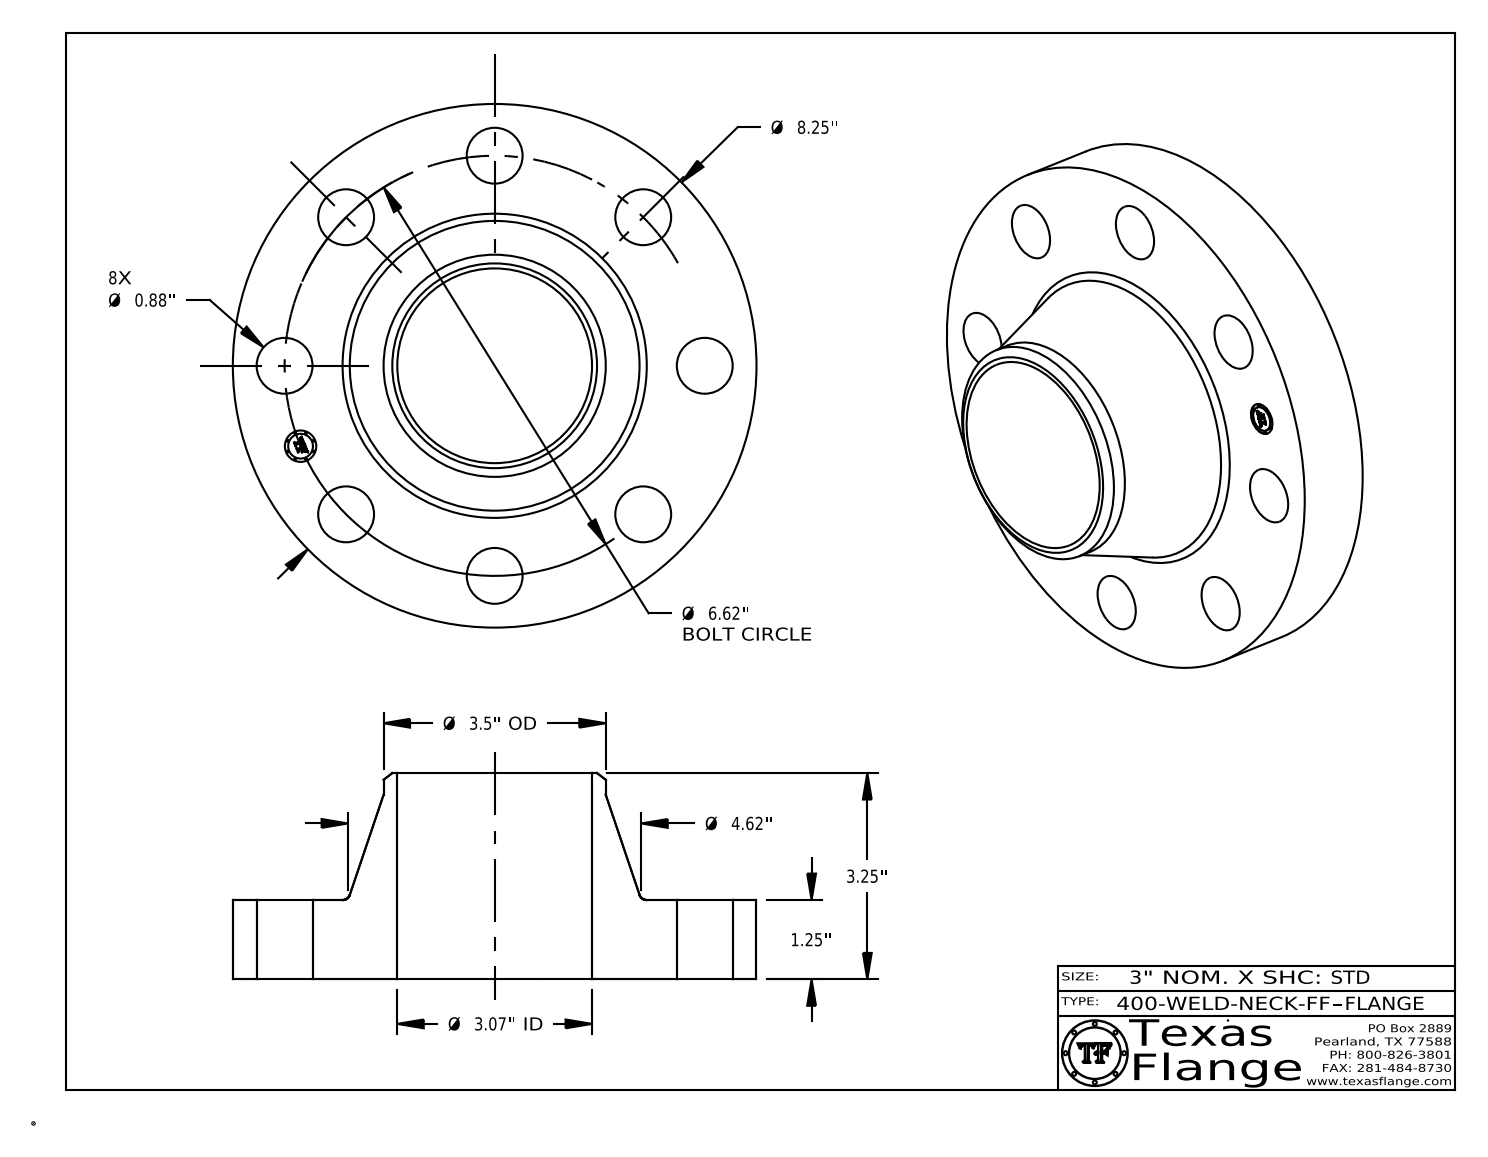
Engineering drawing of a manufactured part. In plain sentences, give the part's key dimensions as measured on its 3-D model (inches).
The part is named "400-WELD-NECK-FF". Its 3-D file was written by "CATIA V5 STEP AP214 (AUTOMOTIVE_DESIGN)". It is 1 solid with 416 faces: 368 planar, 42 cylindrical and 6 other. Overall it measures 8.25 by 8.25 by 3.25 inches. Its volume is 61.55 cubic inches and its surface area 191.7 square inches. Round holes: 8 of diameter 0.88, 1 of diameter 0.495, 1 of diameter 3.068. Round bosses or shafts: 8 of diameter 0.03, 1 of diameter 8.25, 1 of diameter 3.5, 1 of diameter 0.39. The main face-to-face distances are 1.25, 3.25, 2, 0.015, 1.235, 2.015, 0.148, 0.145, 0.027, 0.096. The hole center spacings are 3.31, 2.533, 6.116, 4.681, 4.681, 1.291, 3.678, 6.493.
